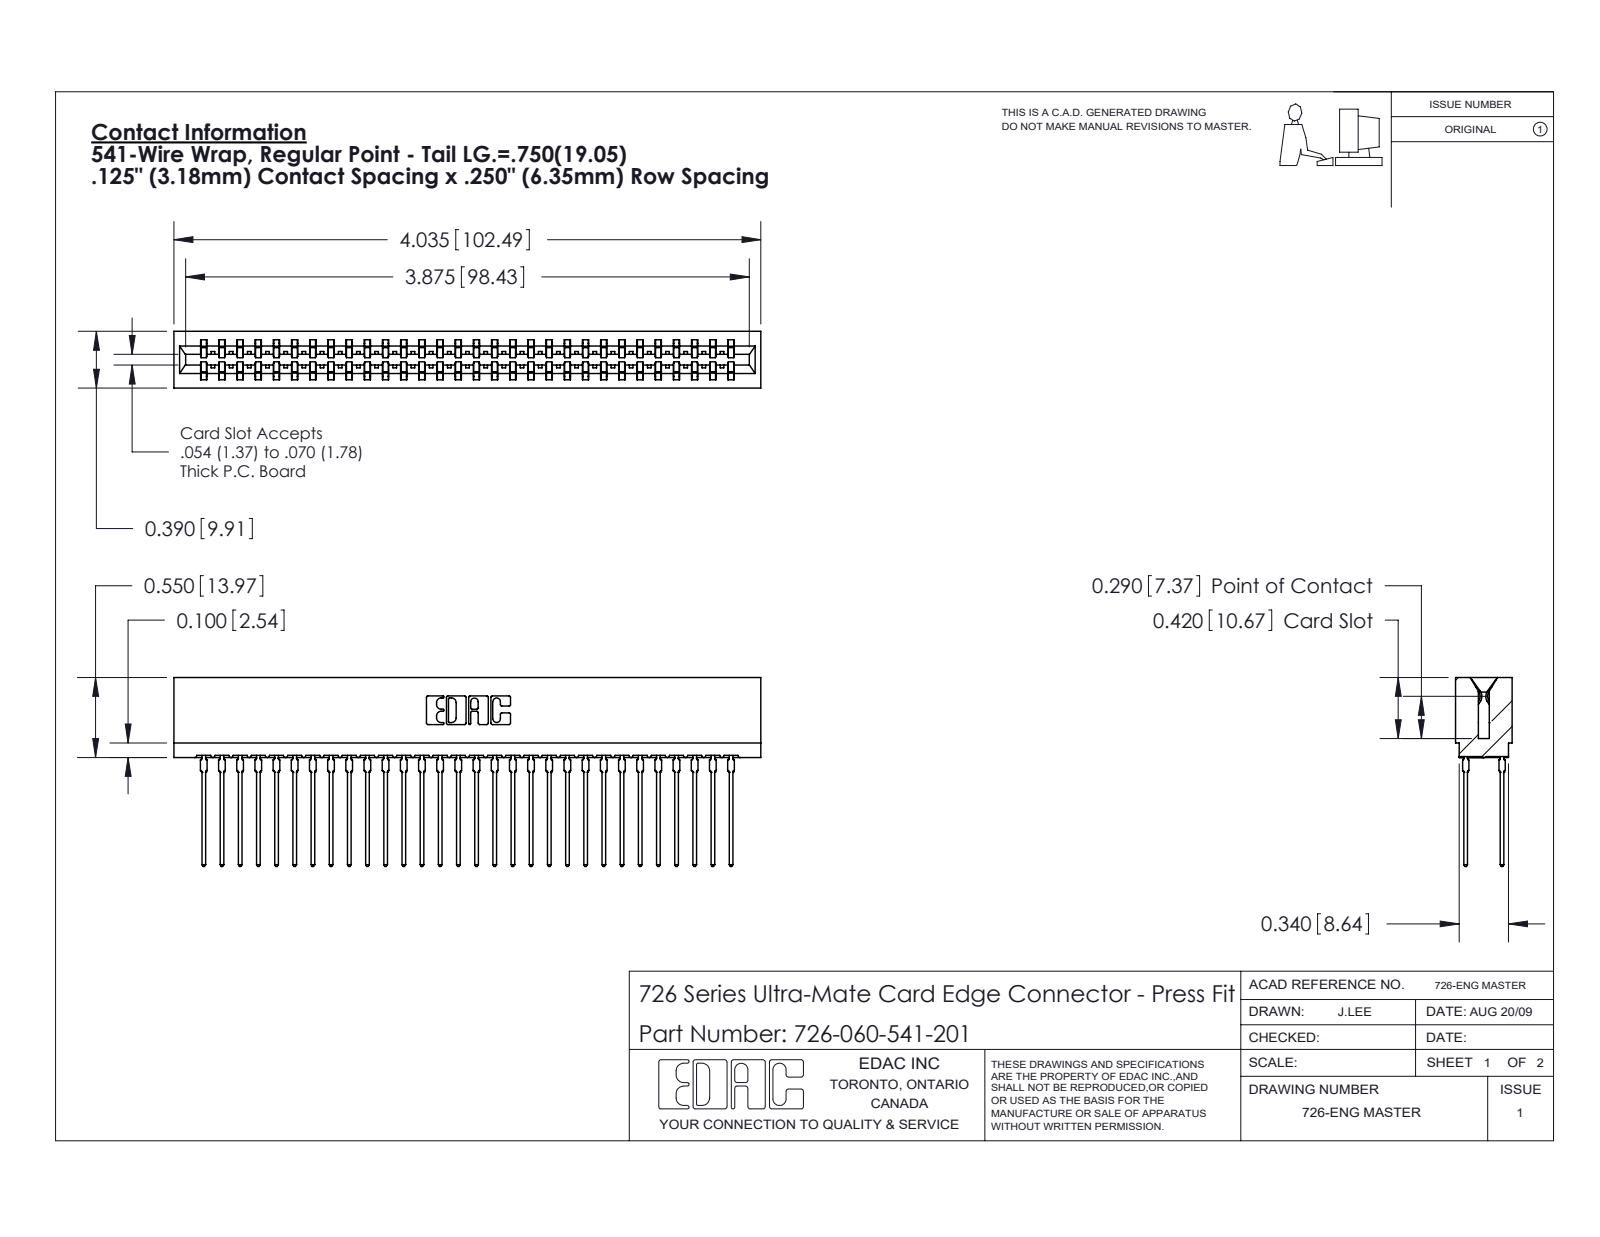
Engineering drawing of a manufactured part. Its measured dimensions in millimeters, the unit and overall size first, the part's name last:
Units: millimetres
Overall size (bounding box): 102.5 × 33 × 9.9
Partial cylindrical surfaces — rounded edges, fillets, slot ends (radius × count): R0.5 ×120, R0.4 ×31, R0.3 ×22, R0.1 ×8, R0.3 ×8, R0.2 ×6, R0.8 ×6, R0.7 ×3
Main face-to-face distances: 1.4, 8.5, 6.4, 0.6, 7.8, 2.1, 9.9, 7, 12.7, 5.7
Volume: 9 820 mm³ · Surface area: 17 690 mm²
Bodies: 61 solids, 5467 faces (2815 planar, 1092 cylindrical, 1560 other)
Part name (STEP PRODUCT): 746-292-001_541; 726-060-541-201; 726 Part_.515 Slot Depth - 01
STEP written by: SolidWorks 2020 (CONFIG_CONTROL_DESIGN)
